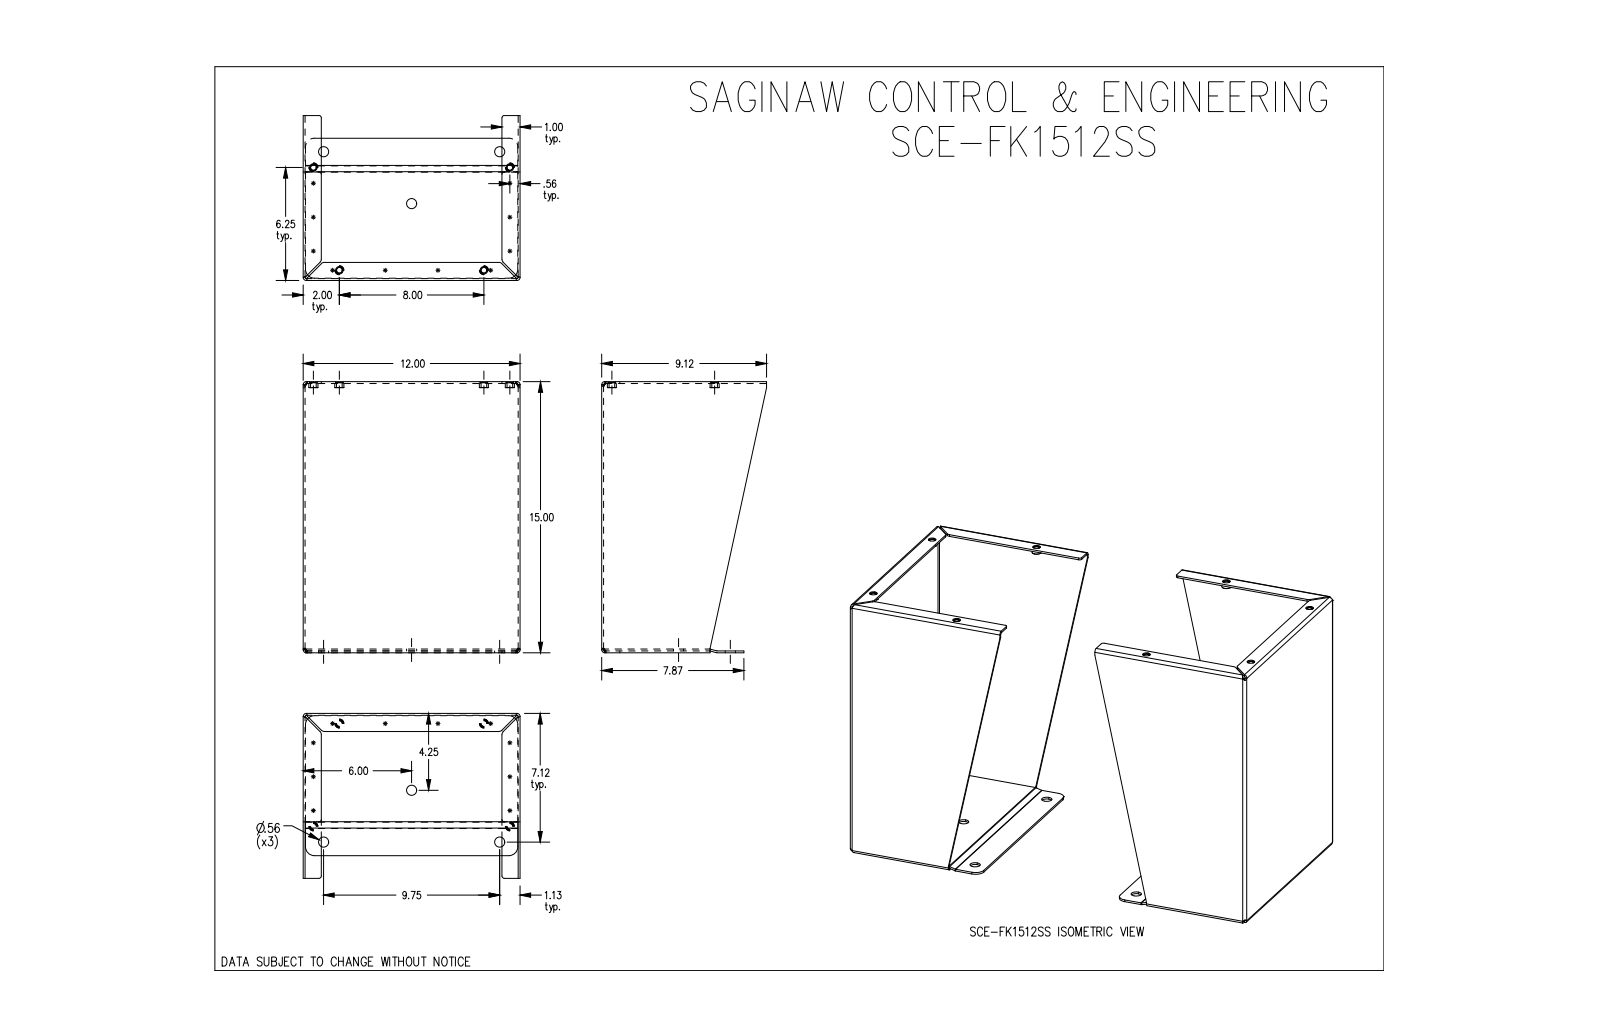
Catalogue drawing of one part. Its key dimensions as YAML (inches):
part_name: "SCE-FK1512SS"
step_written_by: "SolidWorks 2019 (CONFIG_CONTROL_DESIGN)"
units: inches
bodies: {solids: 12, faces: 286, planar: 120, cylindrical: 110, other: 56}
overall_size: [24, 15, 12]
volume: 111.2
surface_area: 2170
round_holes:
  - {diameter: 0.312, count: 8}
  - {diameter: 0.413, count: 8}
  - {diameter: 0.563, count: 6}
round_bosses_or_shafts:
  - {diameter: 0.5, count: 8}
  - {diameter: 0.412, count: 8}
partial_cylinders:
  - {radius: 0.166, count: 16}
  - {radius: 0.062, count: 12}
  - {radius: 0.125, count: 8}
  - {radius: 0.22, count: 8}
  - {radius: 0.5, count: 8}
  - {radius: 0.063, count: 4}
face_to_face_distances: [0.104, 11.896, 23.896, 12, 11.792, 23.792, 24, 14.792, 14.896, 0.101]
hole_center_spacings: [1.035, 5.441, 5.656, 5.793, 5.866, 6.614, 10.646, 11.019]
